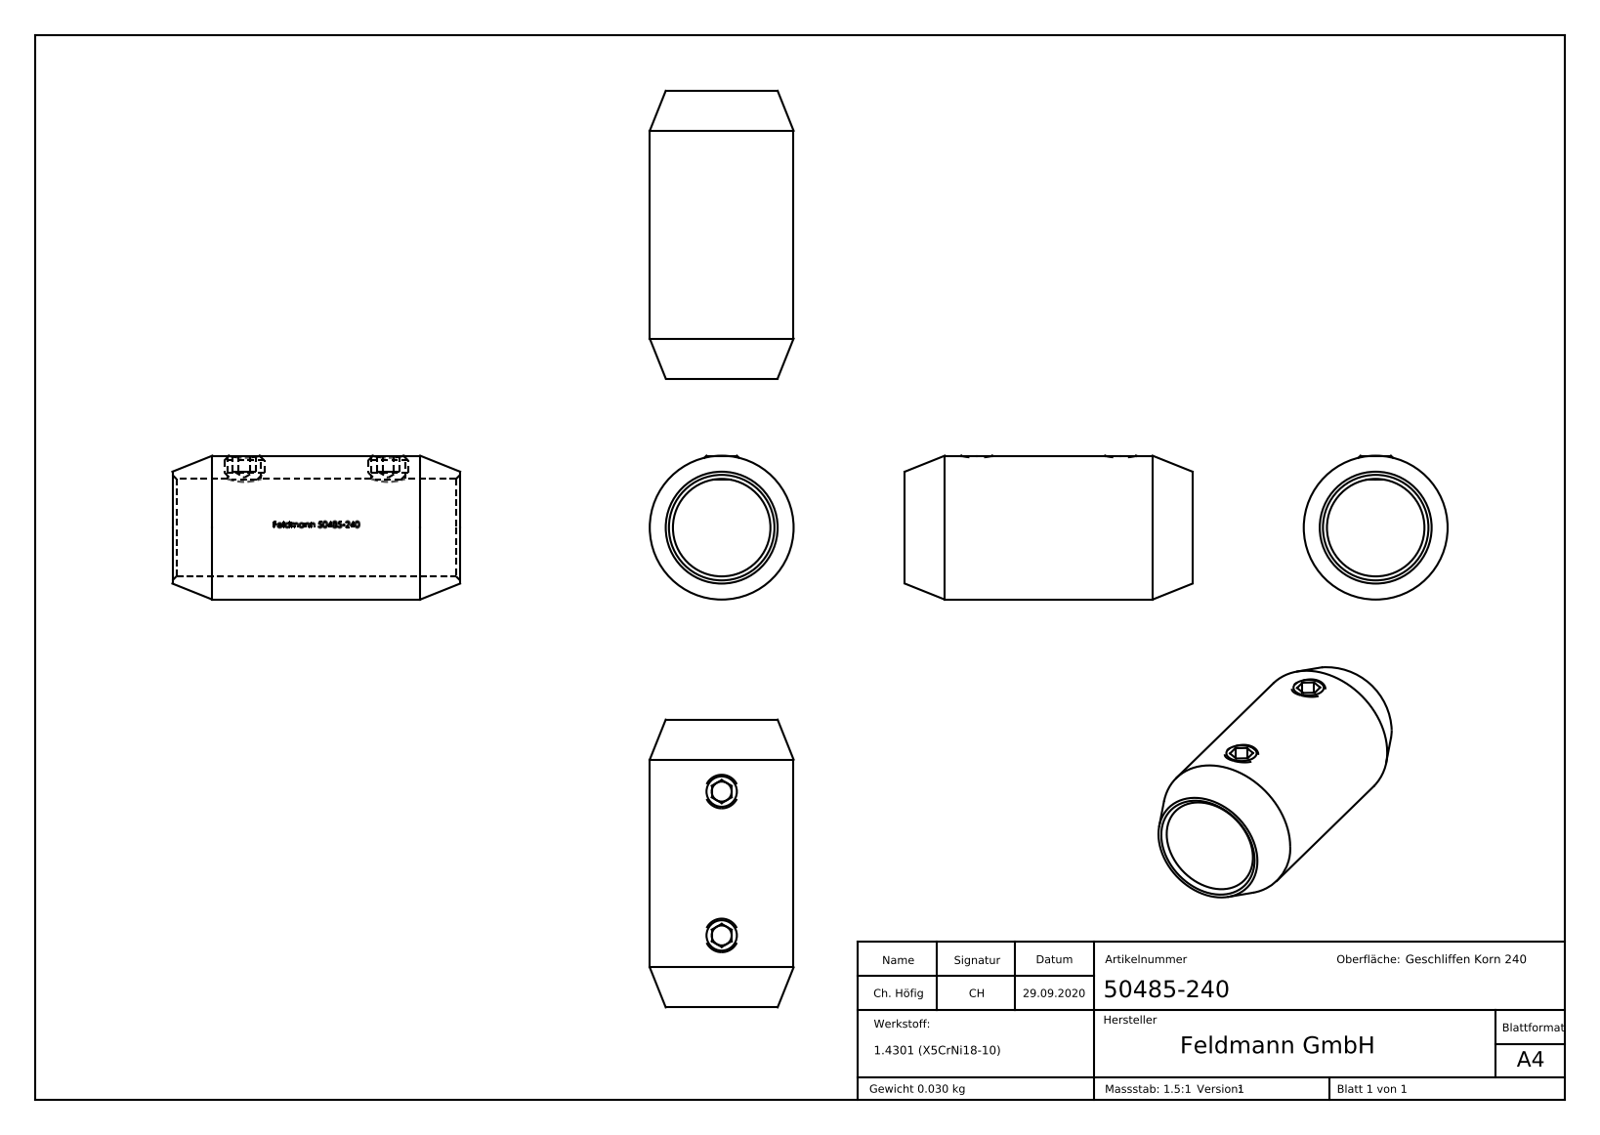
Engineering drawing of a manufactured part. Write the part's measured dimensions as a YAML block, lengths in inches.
part_name: "50485-240; DIN913; 5048X-240 Teil1_50485-240 Teil1; 5048X-240 Teil1 (+1 more)"
step_written_by: "SolidWorks 2018 (CONFIG_CONTROL_DESIGN)"
units: inches
bodies: {solids: 3, faces: 301, planar: 132, cylindrical: 44, other: 125}
overall_size: [2755.906, 196.85, 196.85]
volume: 0.269
surface_area: 5.658
round_holes:
  - {diameter: 0.165, count: 2}
  - {diameter: 0.48, count: 1}
round_bosses_or_shafts:
  - {diameter: 0.197, count: 2}
  - {diameter: 0.709, count: 1}
partial_cylinders:
  - {radius: 0.244, count: 1}
face_to_face_distances: [0.098, 1.417, 0.118, 0.613, 0.712, 0.515, 0.039, 0.079, 0.205, 0.021]
hole_center_spacings: [0.709]
